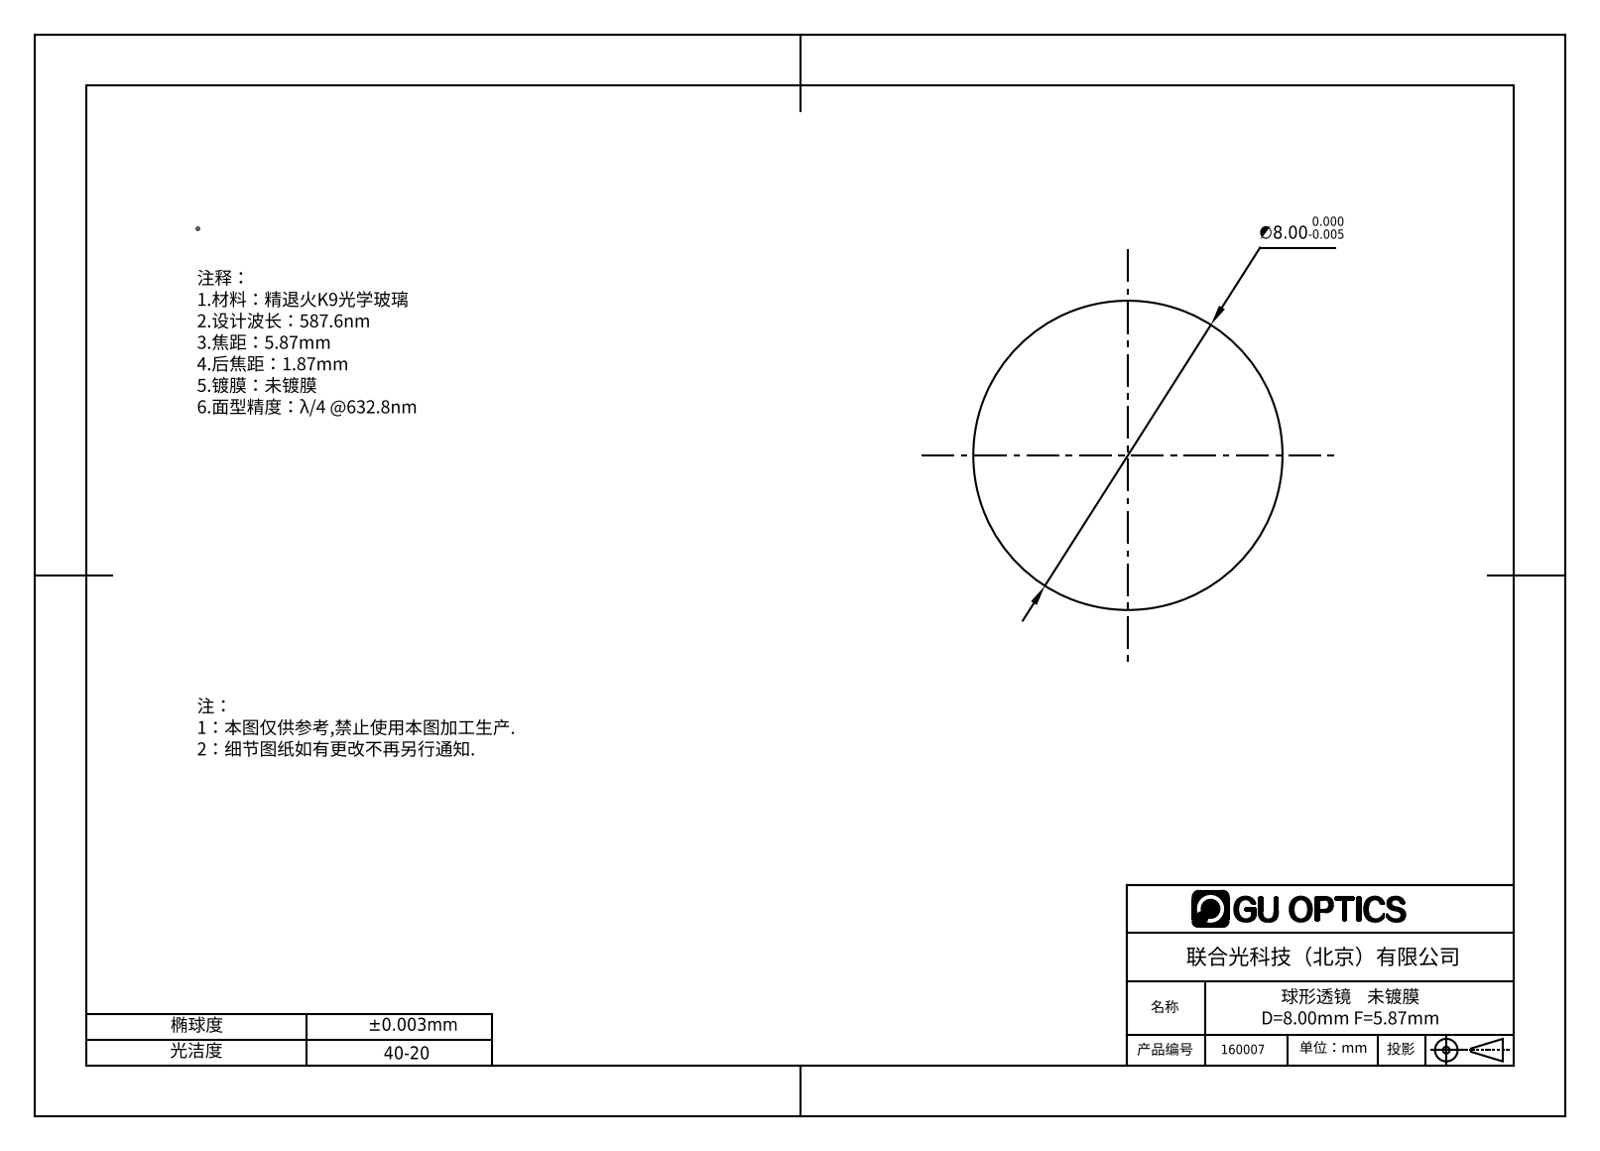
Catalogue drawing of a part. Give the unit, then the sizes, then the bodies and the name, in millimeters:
Units: millimetres
Overall size (bounding box): 8 × 8 × 8
Volume: 268 mm³ · Surface area: 201 mm²
Bodies: 1 solid, 2 faces (0 planar, 0 cylindrical, 2 other)
Part name (STEP PRODUCT): 160007
STEP written by: SolidWorks 2016 (CONFIG_CONTROL_DESIGN)
